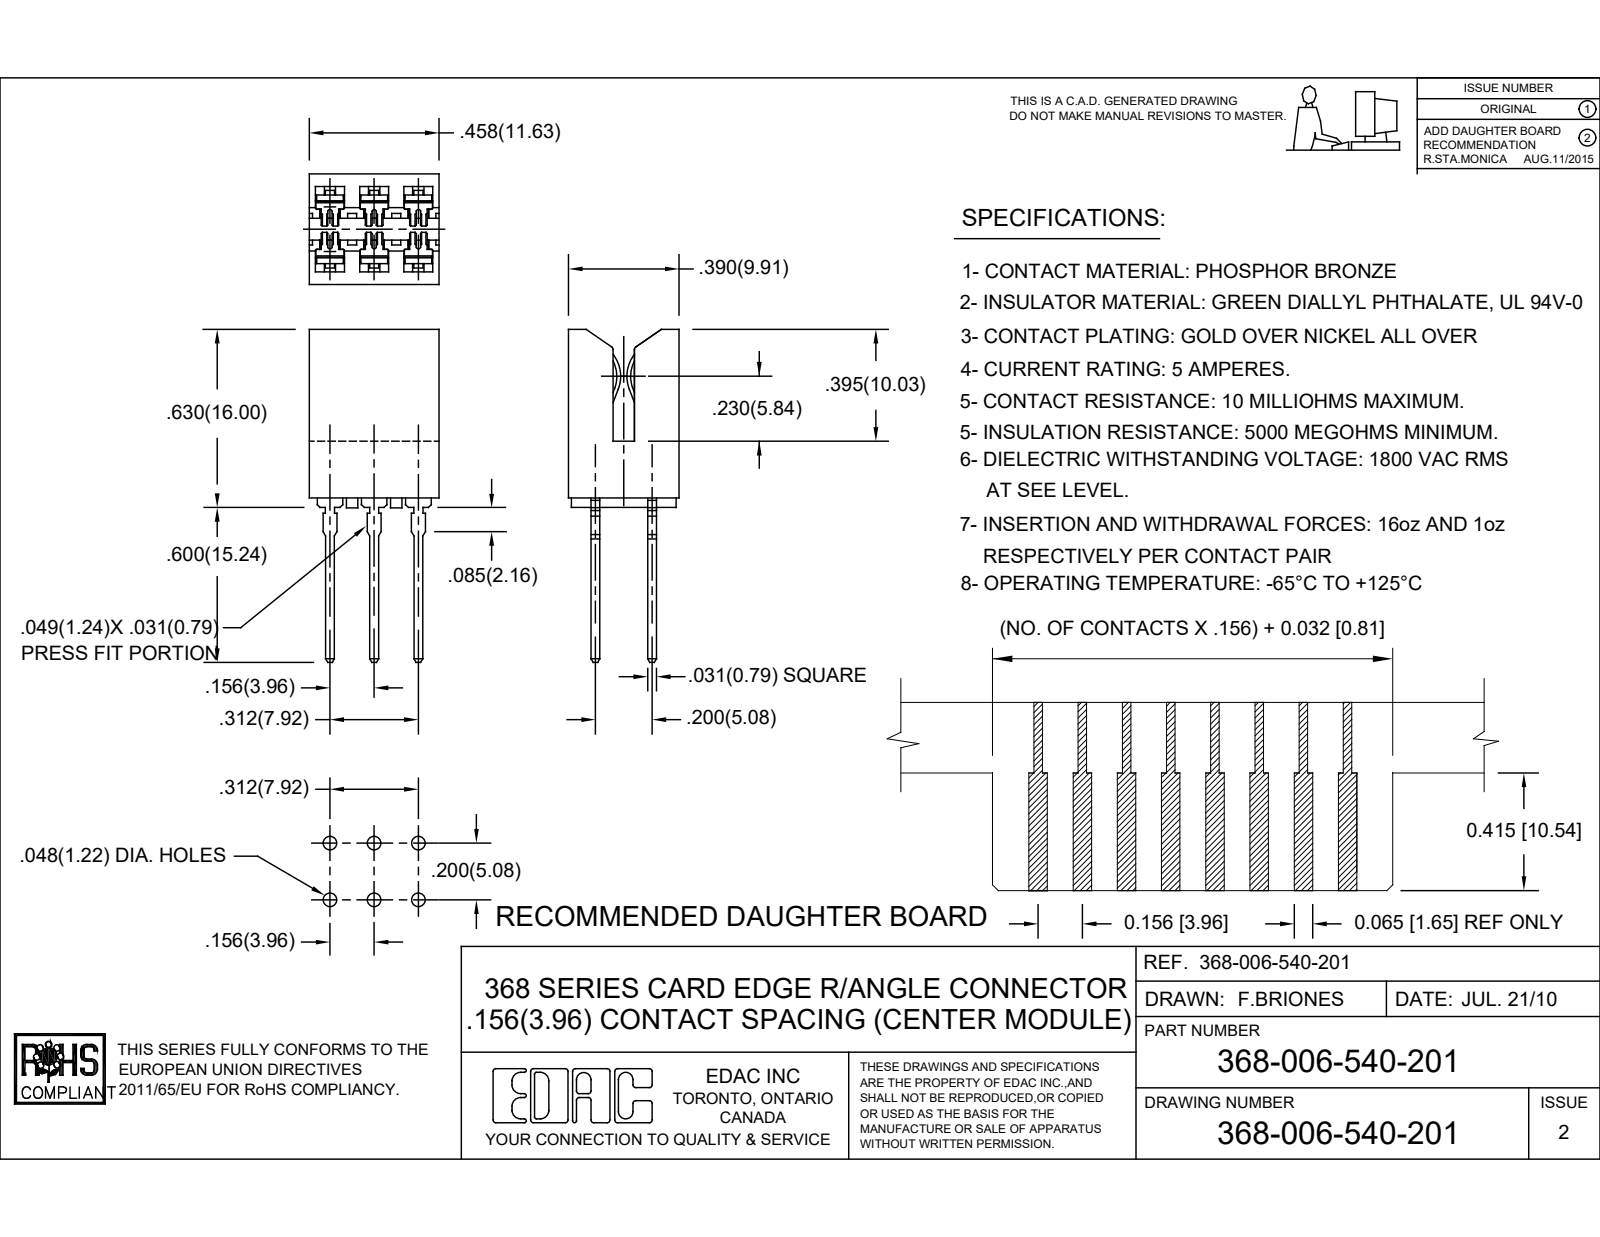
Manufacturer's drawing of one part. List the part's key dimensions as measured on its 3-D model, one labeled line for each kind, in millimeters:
Part name (STEP PRODUCT): 368-290-002 - (Assy State)_368-290-001; 368-006-540-201; 368-210-001
STEP written by: SolidWorks 2020 (AUTOMOTIVE_DESIGN)
Units: millimetres
Bodies: 7 solids, 560 faces (464 planar, 72 cylindrical, 24 other)
Overall size (bounding box): 32.16 × 11.63 × 9.91
Volume: 1 169 mm³ · Surface area: 2 532 mm²
Round holes (diameter × count): ⌀0.81 ×3
Partial cylindrical surfaces — rounded edges, fillets, slot ends (radius × count): R0.19 ×12, R0.25 ×4, R0.25 ×2, R0.81 ×2, R2.84 ×2, R3.17 ×2
Main face-to-face distances: 3.96, 0.9, 1.69, 9.9, 7.92, 5.08, 11.63, 0.38, 2.21, 0.52
Hole centre spacings: 3.96, 3.97, 7.93
